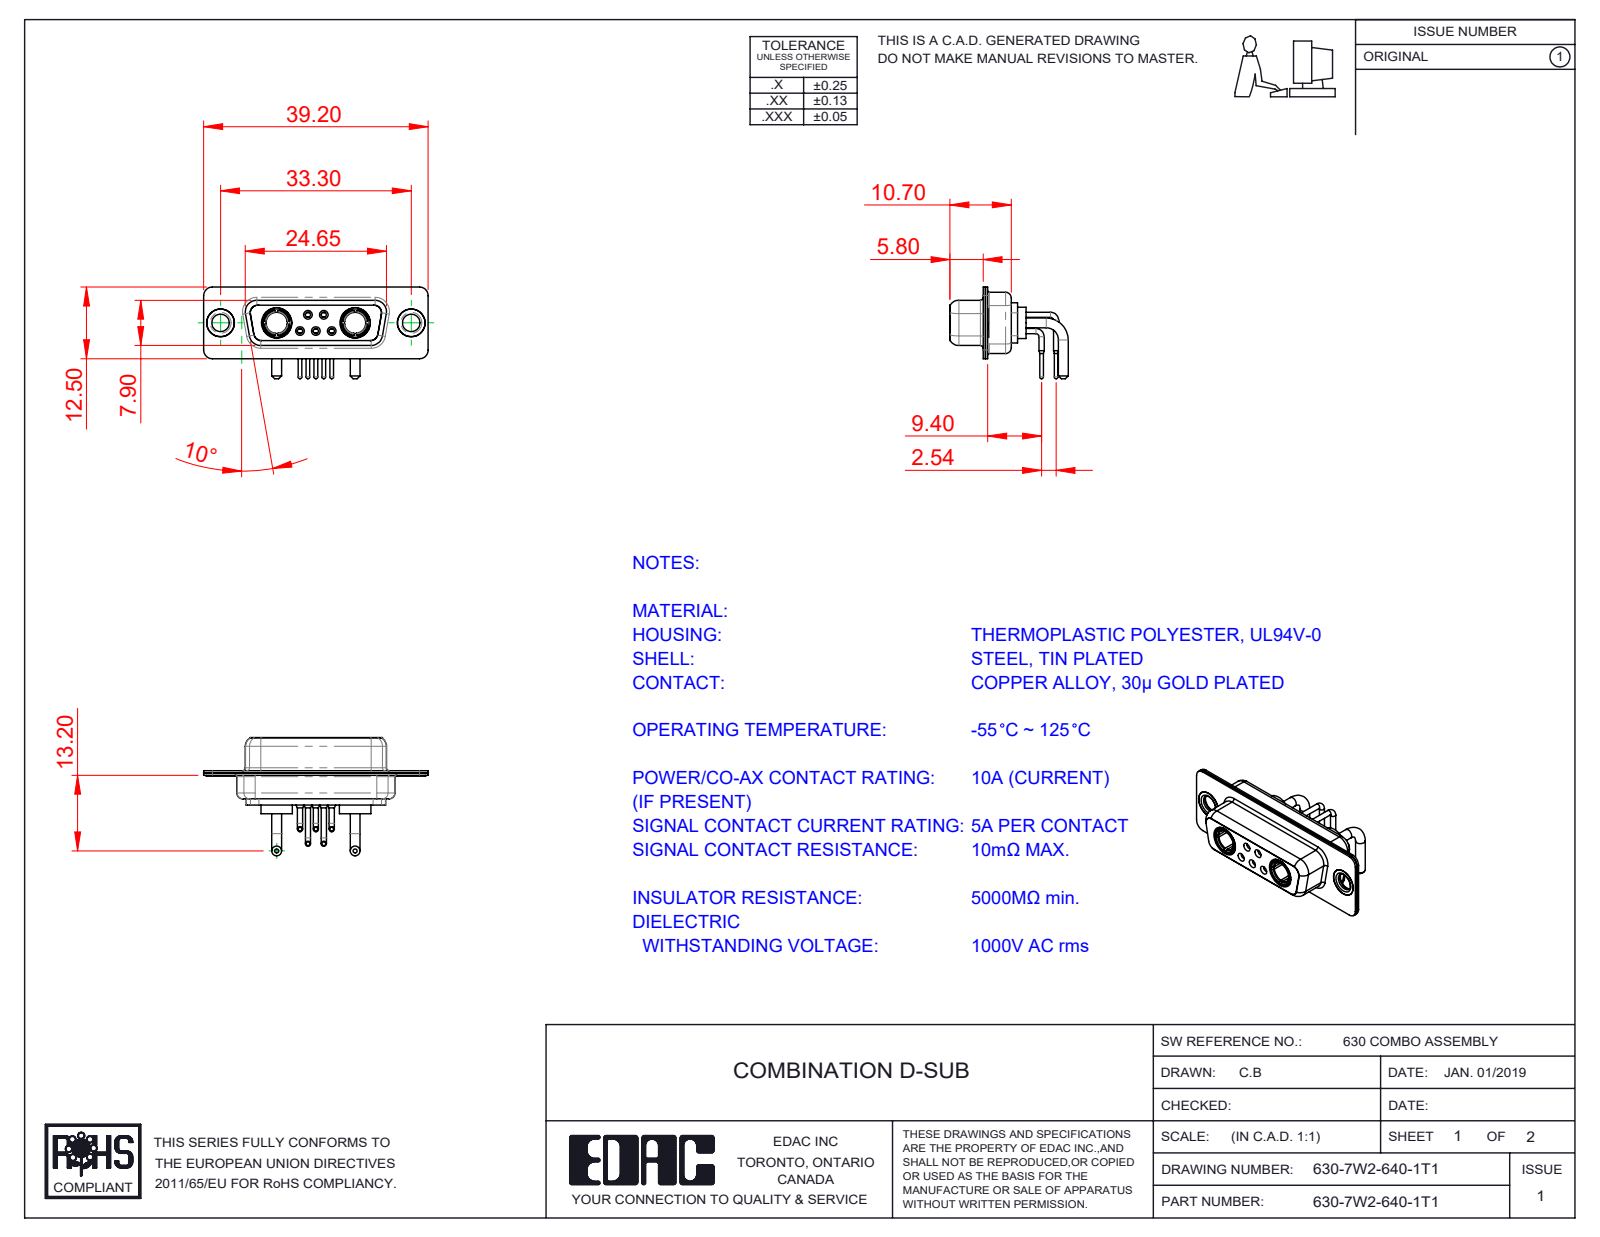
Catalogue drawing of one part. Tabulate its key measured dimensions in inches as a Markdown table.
| quantity | value |
| --- | --- |
| part name | 630Combo Shell Front_15 Contacts; 630Combo Thru Hole Rivet; 630Combo Shell Rear_15 Contacts; 630Combo Contact Row 1 (+4 more) |
| STEP written by | SolidWorks 2020 (CONFIG_CONTROL_DESIGN) |
| units | inches |
| bodies | 14 solids, 674 faces (200 planar, 286 cylindrical, 188 other) |
| overall size | 1.543 × 0.813 × 0.63 |
| volume | 0.149 in³ |
| surface area | 9.046 in² |
| round holes (diameter × count) | 0.035 × 5, 0.043 × 5, 0.059 × 5, 0.079 × 5, 0.191 × 4, 0.063 × 3, 0.067 × 2, 0.12 × 2, 0.146 × 2, 0.157 × 2, 0.159 × 2, 0.209 × 2 |
| round bosses / shafts (diameter × count) | 0.035 × 5, 0.026 × 5, 0.067 × 4, 0.217 × 2, 0.205 × 2, 0.197 × 2, 0.195 × 2, 0.195 × 2 |
| partial cylindrical surfaces (radius × count) | 0.059 × 16, 0.053 × 12, 0.079 × 12, 0.063 × 8, 0.01 × 4, 0.02 × 4, 0.024 × 4, 0.026 × 4 |
| main face-to-face distances | 0.016, 0.055, 0.018, 0.333, 0.35, 0.071, 0.031, 0.244, 0.278, 0.295 |
| hole center spacings | 0.124, 0.109, 0.386, 0.925, 0.17, 0.17, 0.198, 0.198 |
